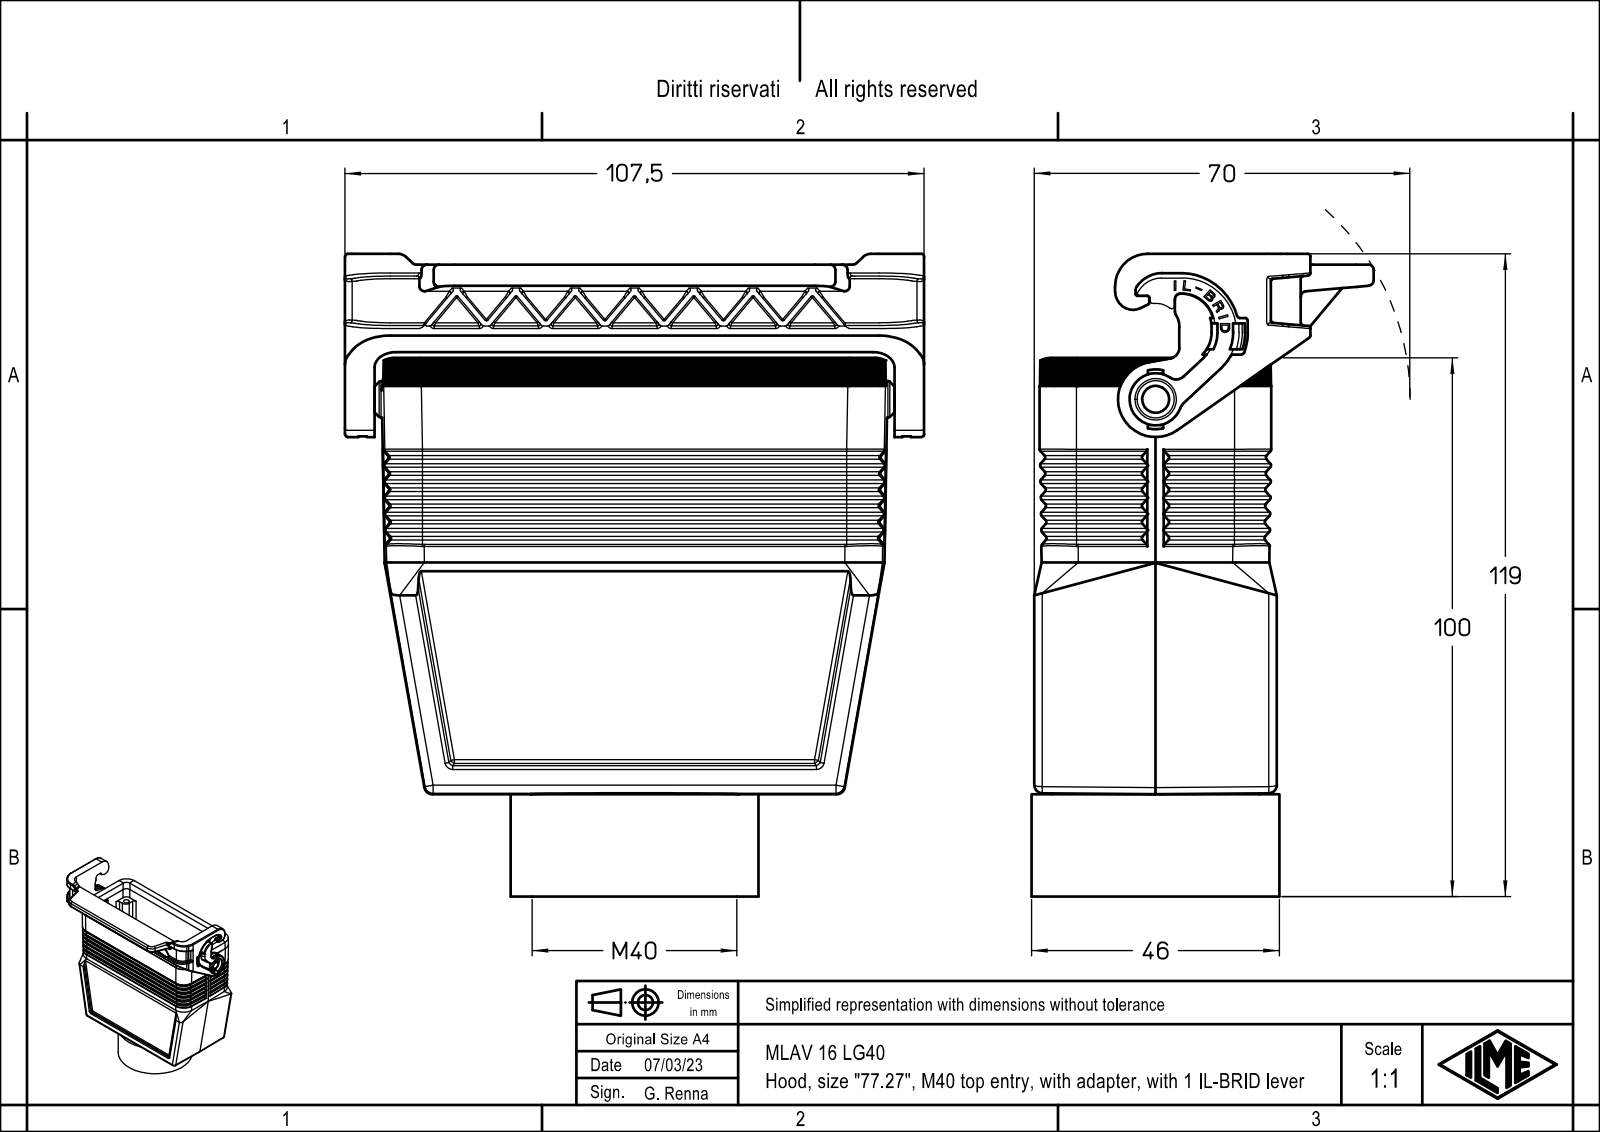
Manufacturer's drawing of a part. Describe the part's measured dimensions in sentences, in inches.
The part is named "MLAV 16 LG40". Its 3-D file was written by "Creo Elements/Direct Modeling 20.1B 02-Apr-2019 (C) Parametric Technology GmbH (AUTOMOTIVE_DESIGN)". It is 1 solid with 1415 faces: 791 planar, 372 cylindrical and 252 other. Overall it measures 4.695 by 4.232 by 2.5 inches. Its volume is 7.251 cubic inches and its surface area 102.2 square inches. Round holes: 4 of diameter 0.118, 4 of diameter 0.138, 1 of diameter 0.128, 1 of diameter 0.213, 1 of diameter 0.303, 1 of diameter 1.339, 1 of diameter 1.52. Round bosses or shafts: 1 of diameter 1.811, 1 of diameter 1.516, 1 of diameter 0.272, 1 of diameter 0.268, 1 of diameter 0.205, 1 of diameter 0.126. Partial cylindrical surfaces (rounded edges, fillets, slot ends): 77 of radius 0.02, 27 of radius 0.004, 23 of radius 0.059, 15 of radius 0.008, 15 of radius 0.039, 14 of radius 0.276, 13 of radius 0.013, 12 of radius 0.118. The main face-to-face distances are 0.148, 1.545, 1.398, 1.693, 0.079, 0.276, 1.821, 0.128, 1.673, 0.039. The hole center spacings are 1.615, 1.063, 3.051, 3.231.
